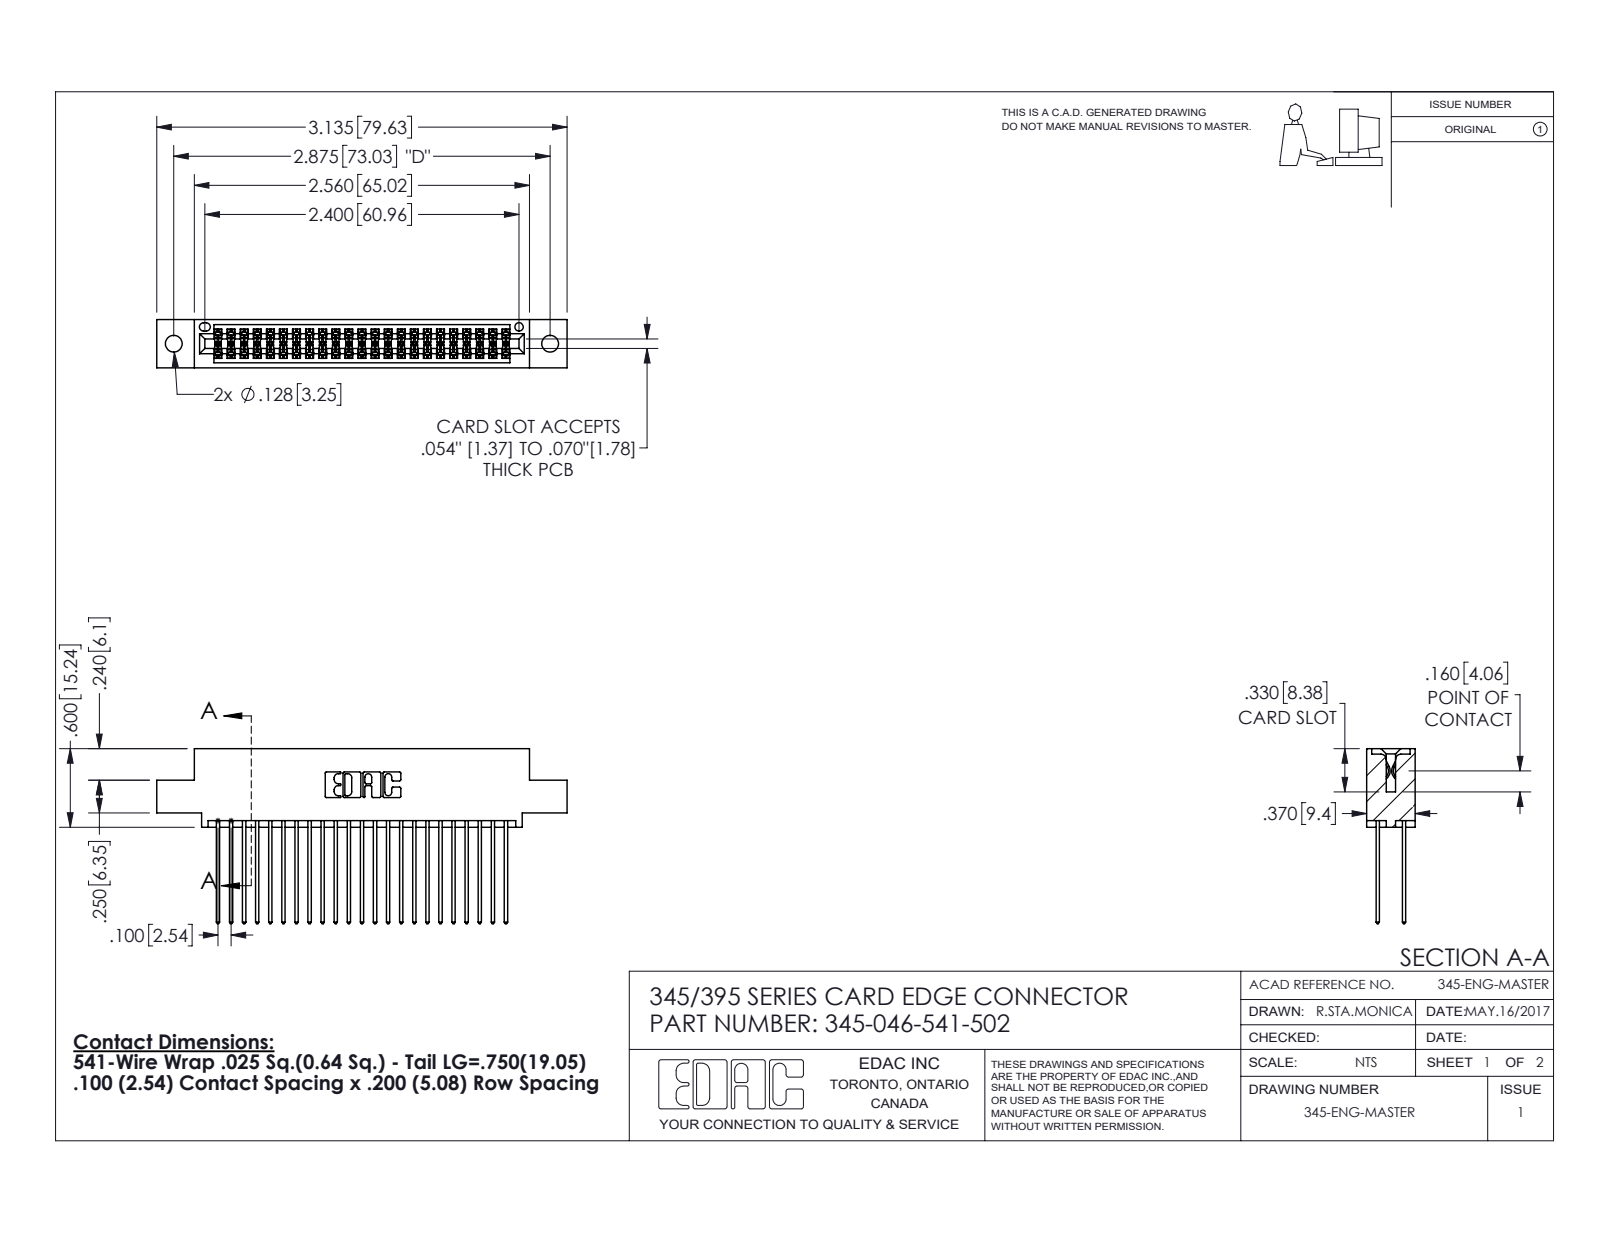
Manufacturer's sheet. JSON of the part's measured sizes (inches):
{"part_name": "345 Part_0.110 Offset - 0.128 Dia; 345-046-541-502; 345-292-001_345-293-141", "step_written_by": "SolidWorks 2016 (CONFIG_CONTROL_DESIGN)", "units": "inches", "bodies": {"solids": 47, "faces": 2430, "planar": 1602, "cylindrical": 828, "other": 0}, "overall_size": [3.135, 1.337, 0.37], "volume_in3": 0.471, "surface_area_in2": 18.74, "round_holes": [[0.128, 2], [0.064, 1]], "partial_cylinders_radius": [[0.006, 69], [0.01, 46], [0.01, 22], [0.007, 6], [0.031, 6], [0.026, 3], [0.014, 2], [0.019, 2]], "face_to_face_distances": [0.298, 0.072, 0.2, 0.098, 0.272, 0.025, 0.37, 0.225, 0.175, 0.149], "hole_center_spacings": [0.27, 2.641, 2.875]}
